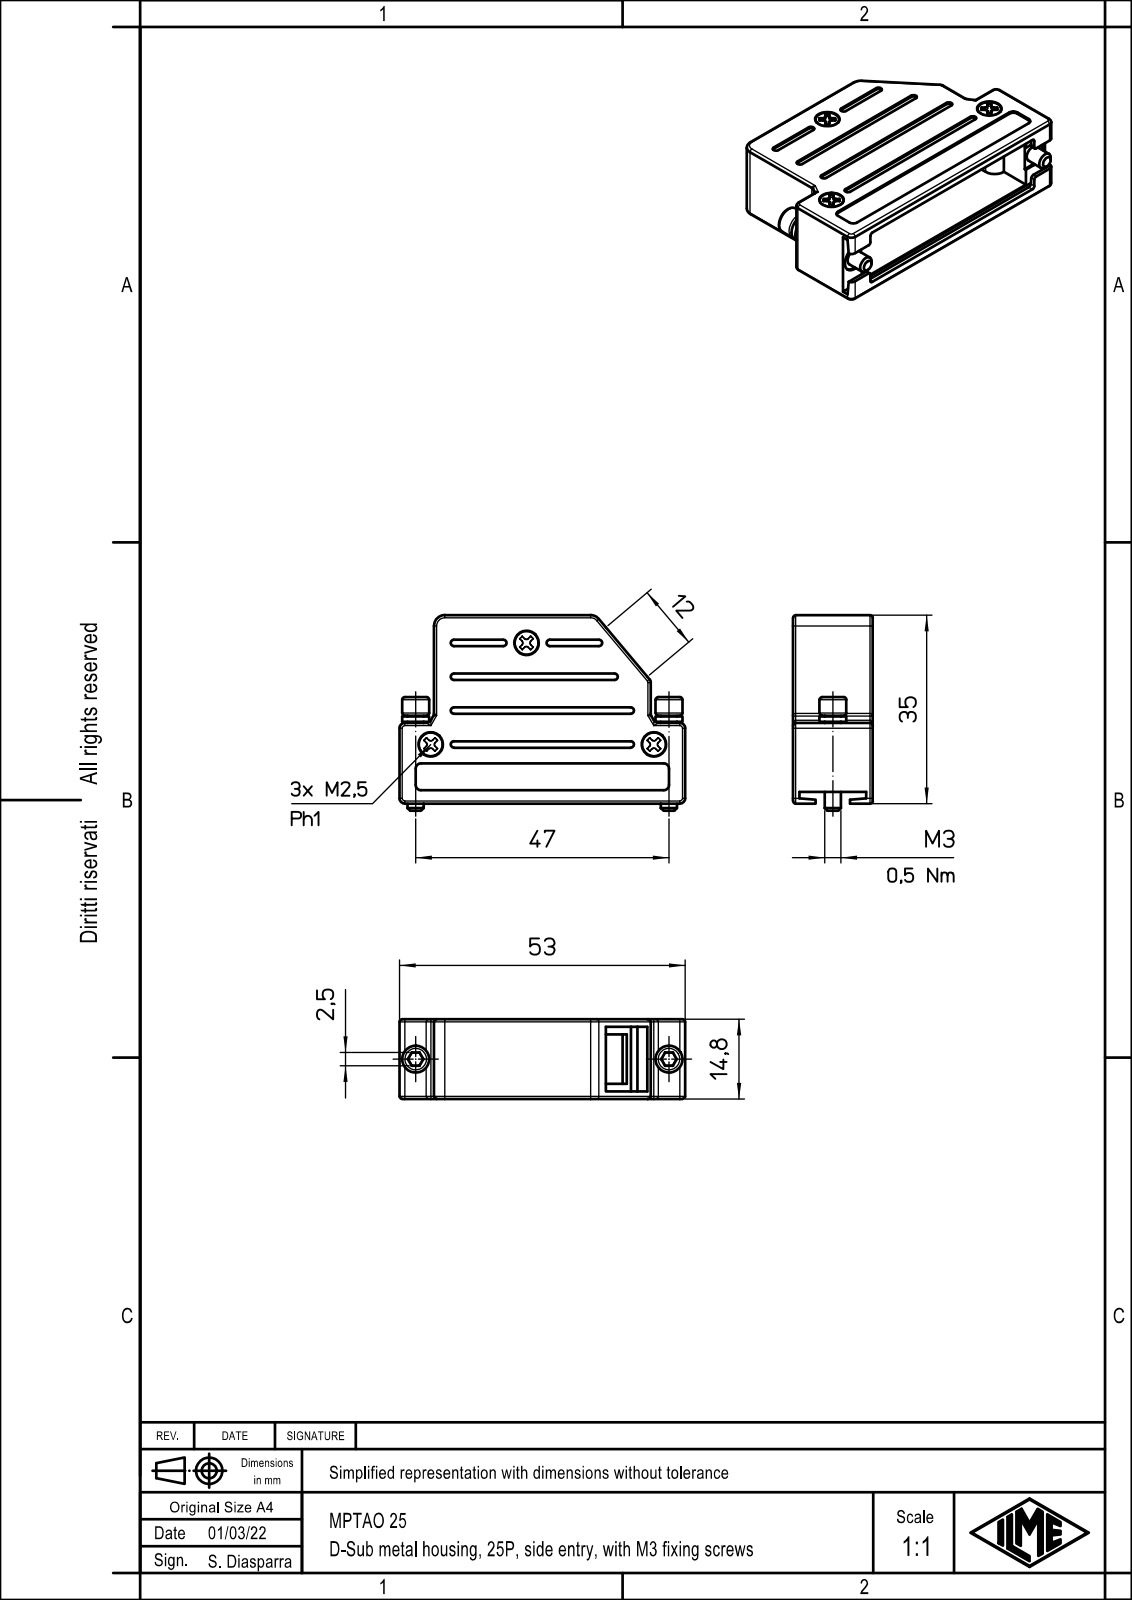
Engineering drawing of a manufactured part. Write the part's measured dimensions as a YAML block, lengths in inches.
part_name: "MPTAO_25"
step_written_by: "Creo Elements/Direct Modeling 20.1B 02-Apr-2019 (C) Parametric Technology GmbH (AUTOMOTIVE_DESIGN)"
units: inches
bodies: {solids: 1, faces: 625, planar: 158, cylindrical: 193, other: 274}
overall_size: [2.087, 1.429, 0.583]
volume: 0.529
surface_area: 14.28
round_bosses_or_shafts:
  - {diameter: 0.197, count: 2}
  - {diameter: 0.118, count: 2}
partial_cylinders:
  - {radius: 0.02, count: 40}
  - {radius: 0.039, count: 13}
  - {radius: 0.024, count: 10}
  - {radius: 0.079, count: 2}
  - {radius: 0.081, count: 2}
  - {radius: 0.094, count: 2}
face_to_face_distances: [0.524, 0.059, 0.465, 0.583, 0.047, 0.512, 0.516, 0.051, 0.563, 0.571]
